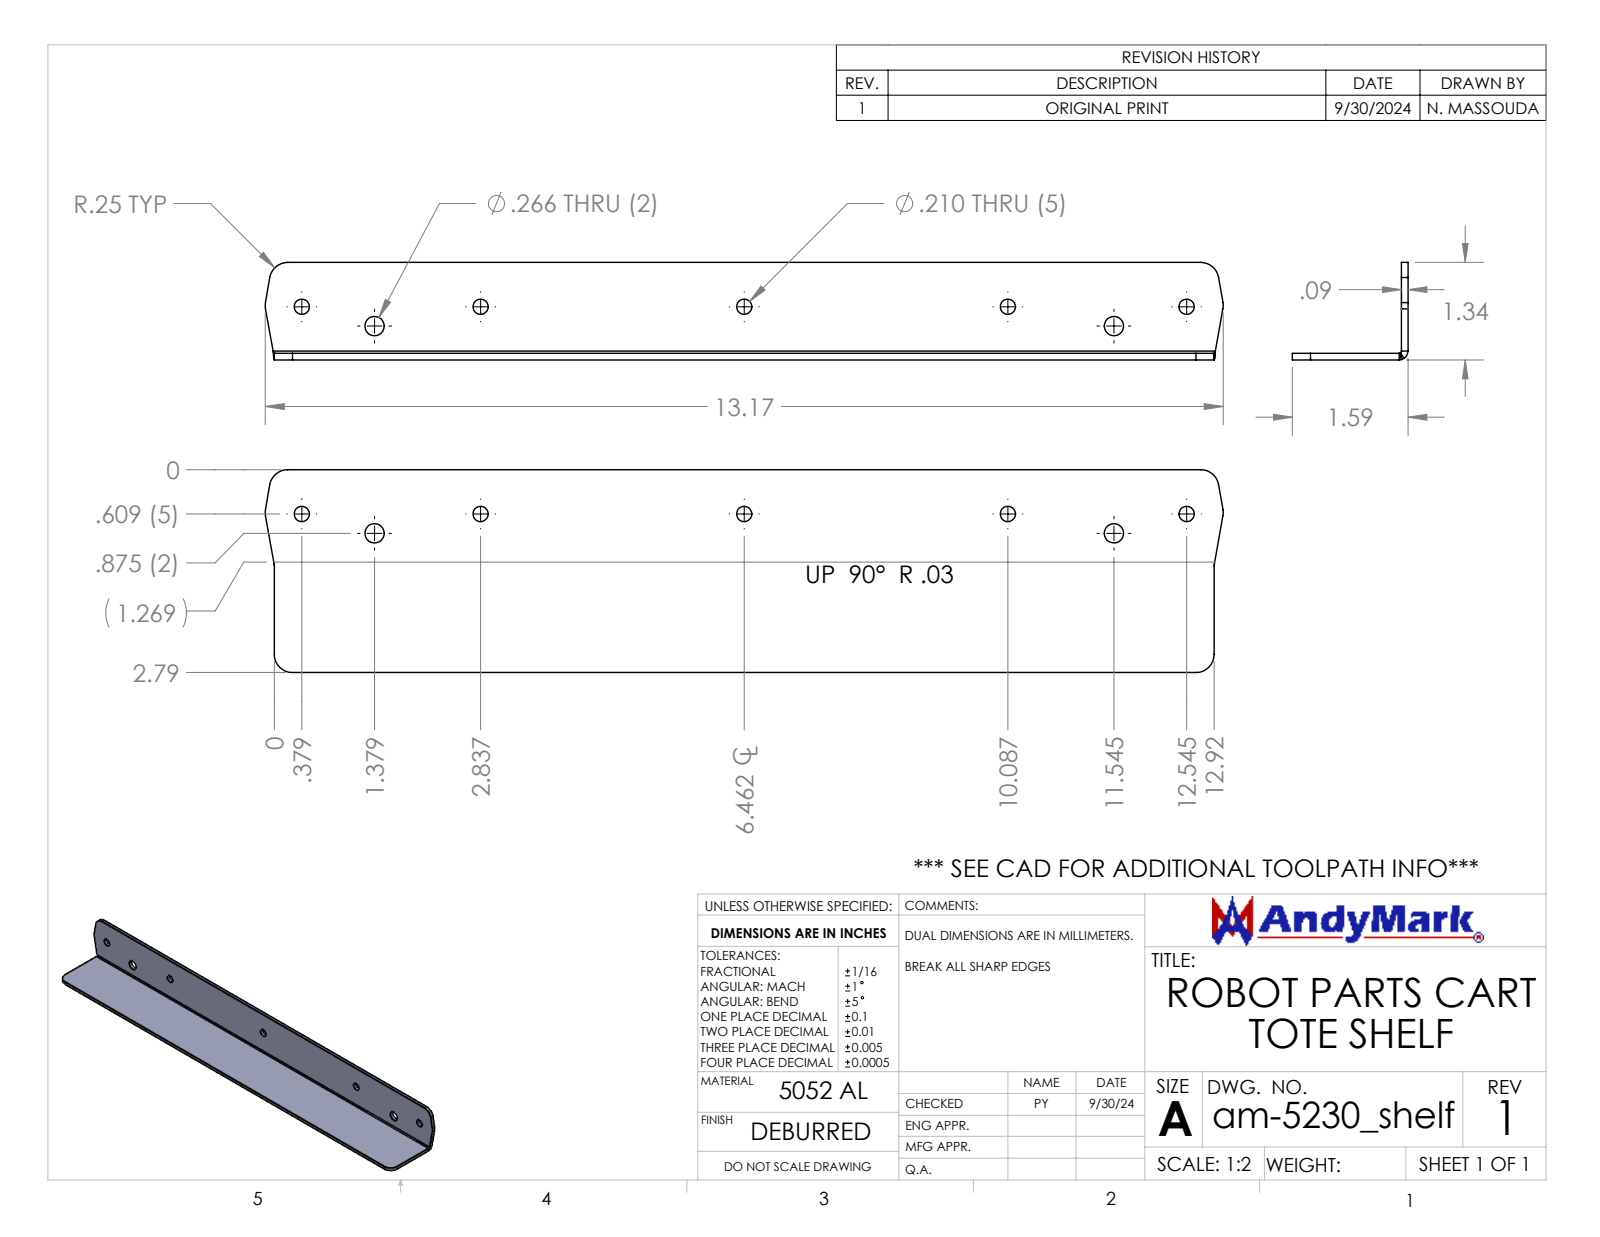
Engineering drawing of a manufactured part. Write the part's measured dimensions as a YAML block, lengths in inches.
part_name: "am-5230_shelf Robot Parts Cart Shelf"
step_written_by: "SolidWorks 2024 (AUTOMOTIVE_DESIGN)"
units: inches
bodies: {solids: 1, faces: 42, planar: 12, cylindrical: 22, other: 8}
overall_size: [13.172, 1.59, 1.34]
volume: 3.252
surface_area: 75.52
round_holes:
  - {diameter: 0.21, count: 5}
  - {diameter: 0.266, count: 2}
partial_cylinders:
  - {radius: 0.25, count: 6}
  - {radius: 0.032, count: 1}
  - {radius: 0.122, count: 1}
face_to_face_distances: [0.09, 1.34, 1.25, 1.5, 1.59, 12.924]
hole_center_spacings: [1.035, 1.482, 2.458, 8.712, 9.708, 11.169, 3.625, 3.625]
